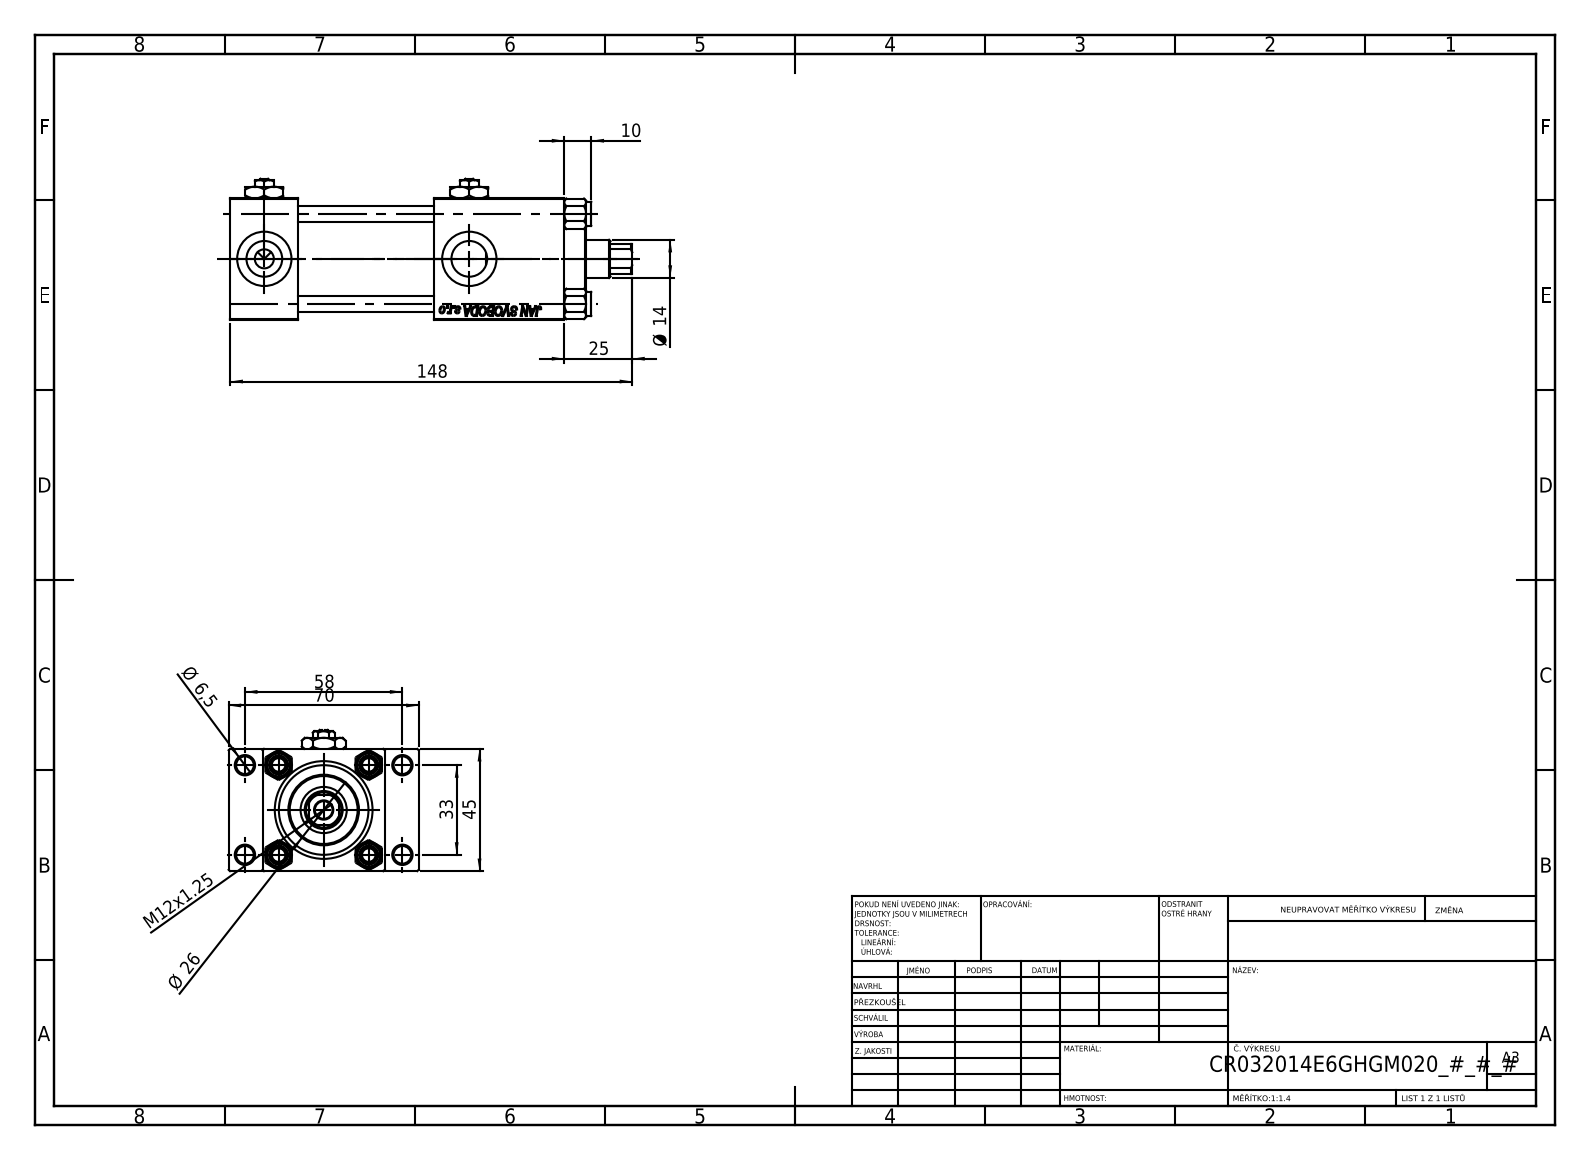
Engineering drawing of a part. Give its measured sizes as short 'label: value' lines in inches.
name: NUT_M5_E; V215CR_E_Body; V215CR_VCP_E; V215_VC_A (+2 more)
written by: SolidWorks 2019 (CONFIG_CONTROL_DESIGN)
unit: in
bodies: 13 solids, 1235 faces (544 planar, 97 cylindrical, 594 other)
size: 5.827 × 2.756 × 2.047
volume: 13.29 in³; area: 121.3 in²
holes: 5× ⌀0.256, 4× ⌀0.236, 4× ⌀0.518, 4× ⌀0.787, 3× ⌀0.276, 1× ⌀0.551, 1× ⌀0.669, 1× ⌀0.945, 1× ⌀1.26, 1× ⌀1.299
bosses: 4× ⌀0.354, 1× ⌀1.496, 1× ⌀1.024
rounds: 1× R0.256
face distances: 1.772, 0.984, 0.492, 2.264, 4.843, 3.858, 1.969, 2.953, 1.89, 3.713
hole spacings: 0.488, 0.924, 1.307, 1.314, 1.392, 1.795, 2.219, 1.299
